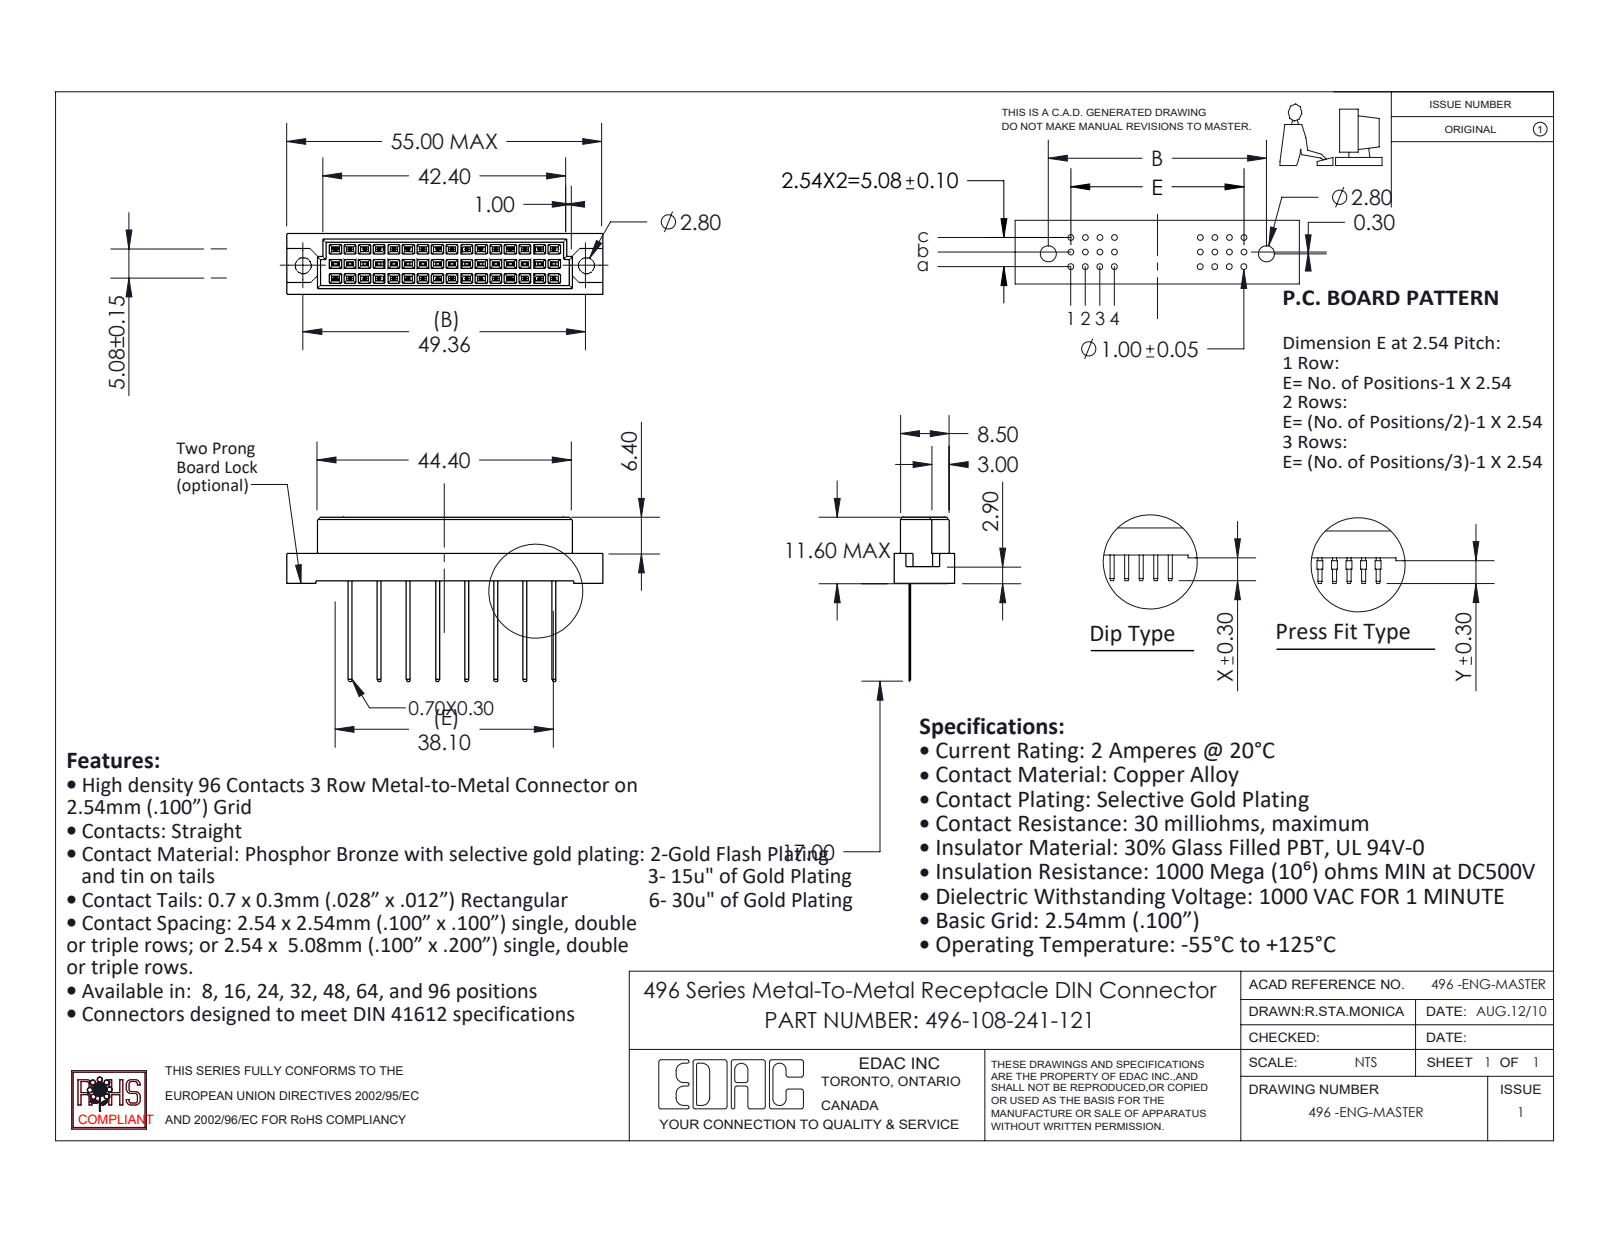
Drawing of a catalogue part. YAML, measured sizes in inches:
part_name: "496-290_41; 496-108-241-121; 496 Part_48"
step_written_by: "SolidWorks 2020 (CONFIG_CONTROL_DESIGN)"
units: inches
bodies: {solids: 9, faces: 746, planar: 742, cylindrical: 4, other: 0}
overall_size: [2.165, 1.126, 0.417]
volume: 0.282
surface_area: 7.076
round_holes:
  - {diameter: 0.11, count: 2}
face_to_face_distances: [0.1, 0.2, 0.041, 0.376, 0.032, 0.417, 0.132, 0.068, 0.335, 0.022]
hole_center_spacings: [1.943]
